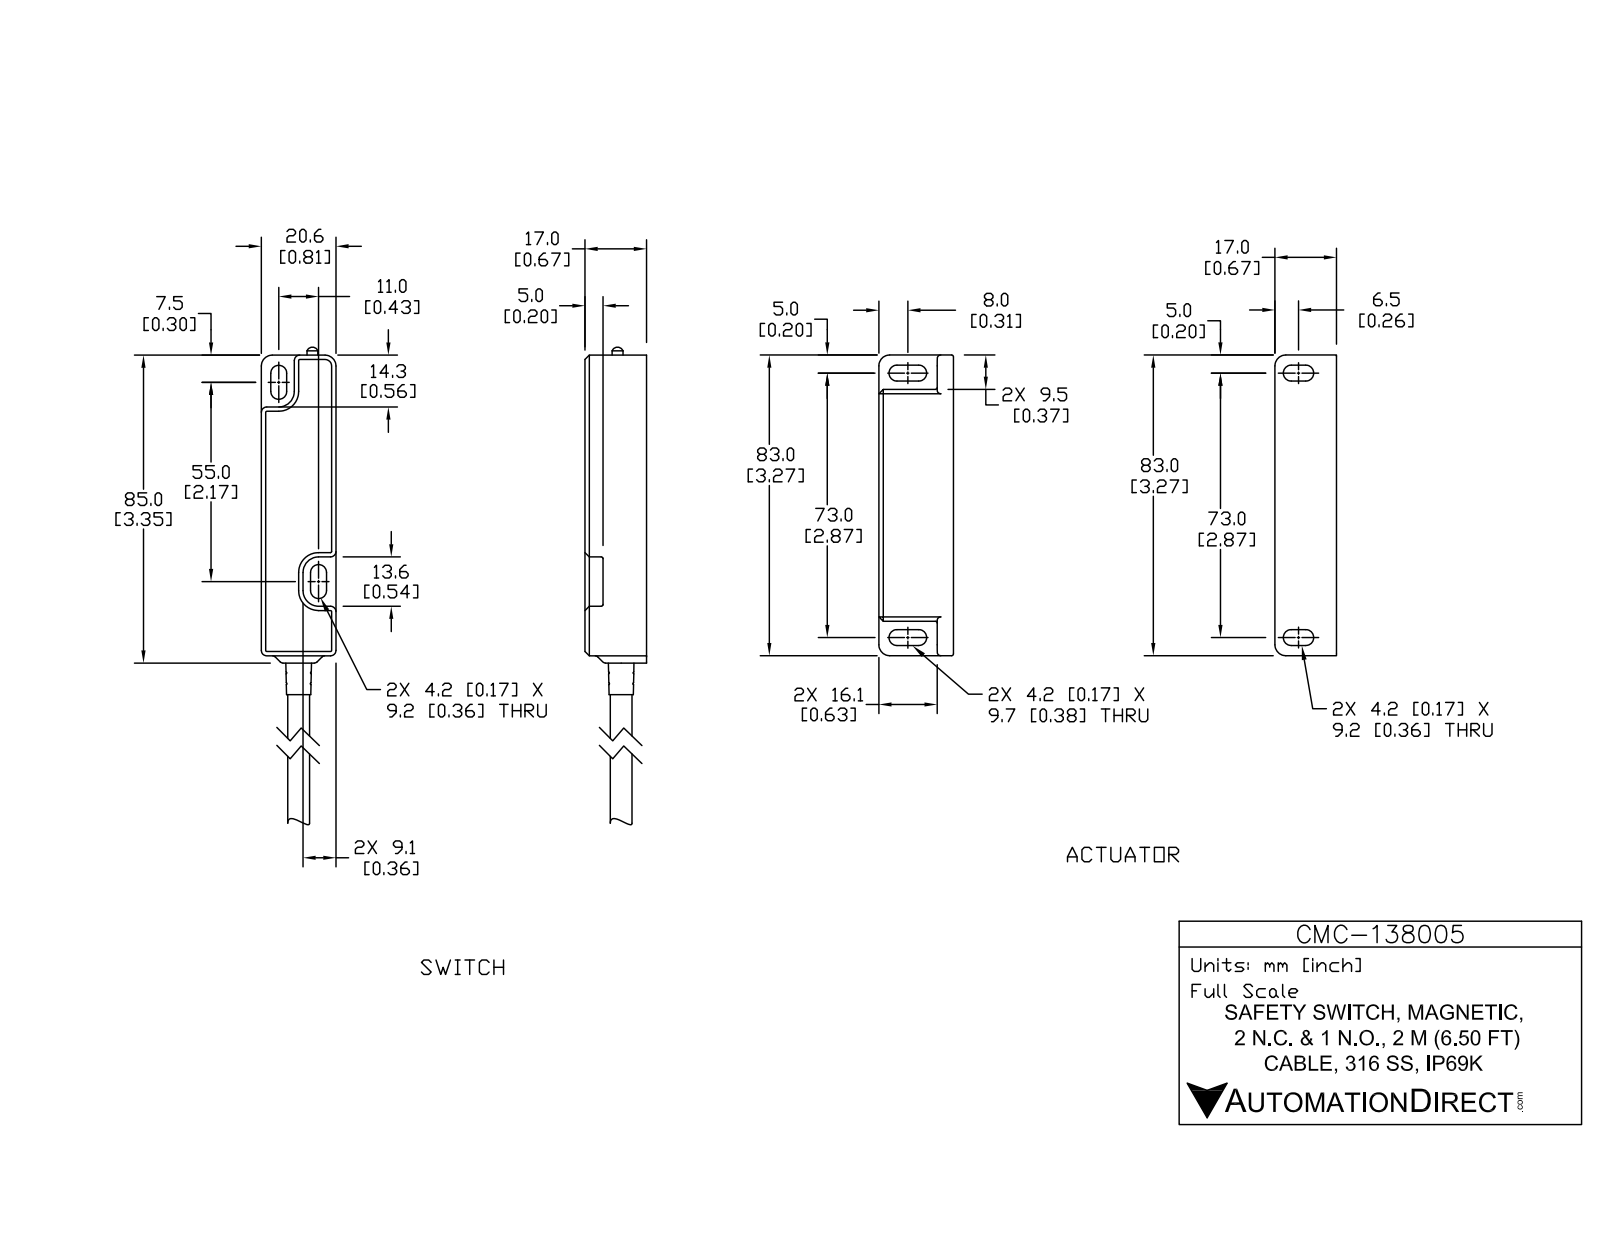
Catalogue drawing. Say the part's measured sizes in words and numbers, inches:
The part is named "CMC-138005; CMC-138005_2; CMC-138005_1". Its 3-D file was written by "SolidWorks 2017 (AUTOMOTIVE_DESIGN)". It is 5 solids with 189 faces: 58 planar, 66 cylindrical and 65 other. Overall it measures 7.255 by 1.378 by 0.811 inches. Its volume is 3.331 cubic inches and its surface area 25.32 square inches. Round bosses or shafts: 1 of diameter 0.236, 1 of diameter 0.118. Partial cylindrical surfaces (rounded edges, fillets, slot ends): 15 of radius 0.02, 15 of radius 0.039, 8 of radius 0.083, 6 of radius 0.059, 4 of radius 0.087, 3 of radius 0.028, 3 of radius 0.118, 3 of radius 0.169. The main face-to-face distances are 0.709, 0.669, 0.811, 0.039, 1.378, 0.177, 0.374, 2.894, 3.268, 0.492.
